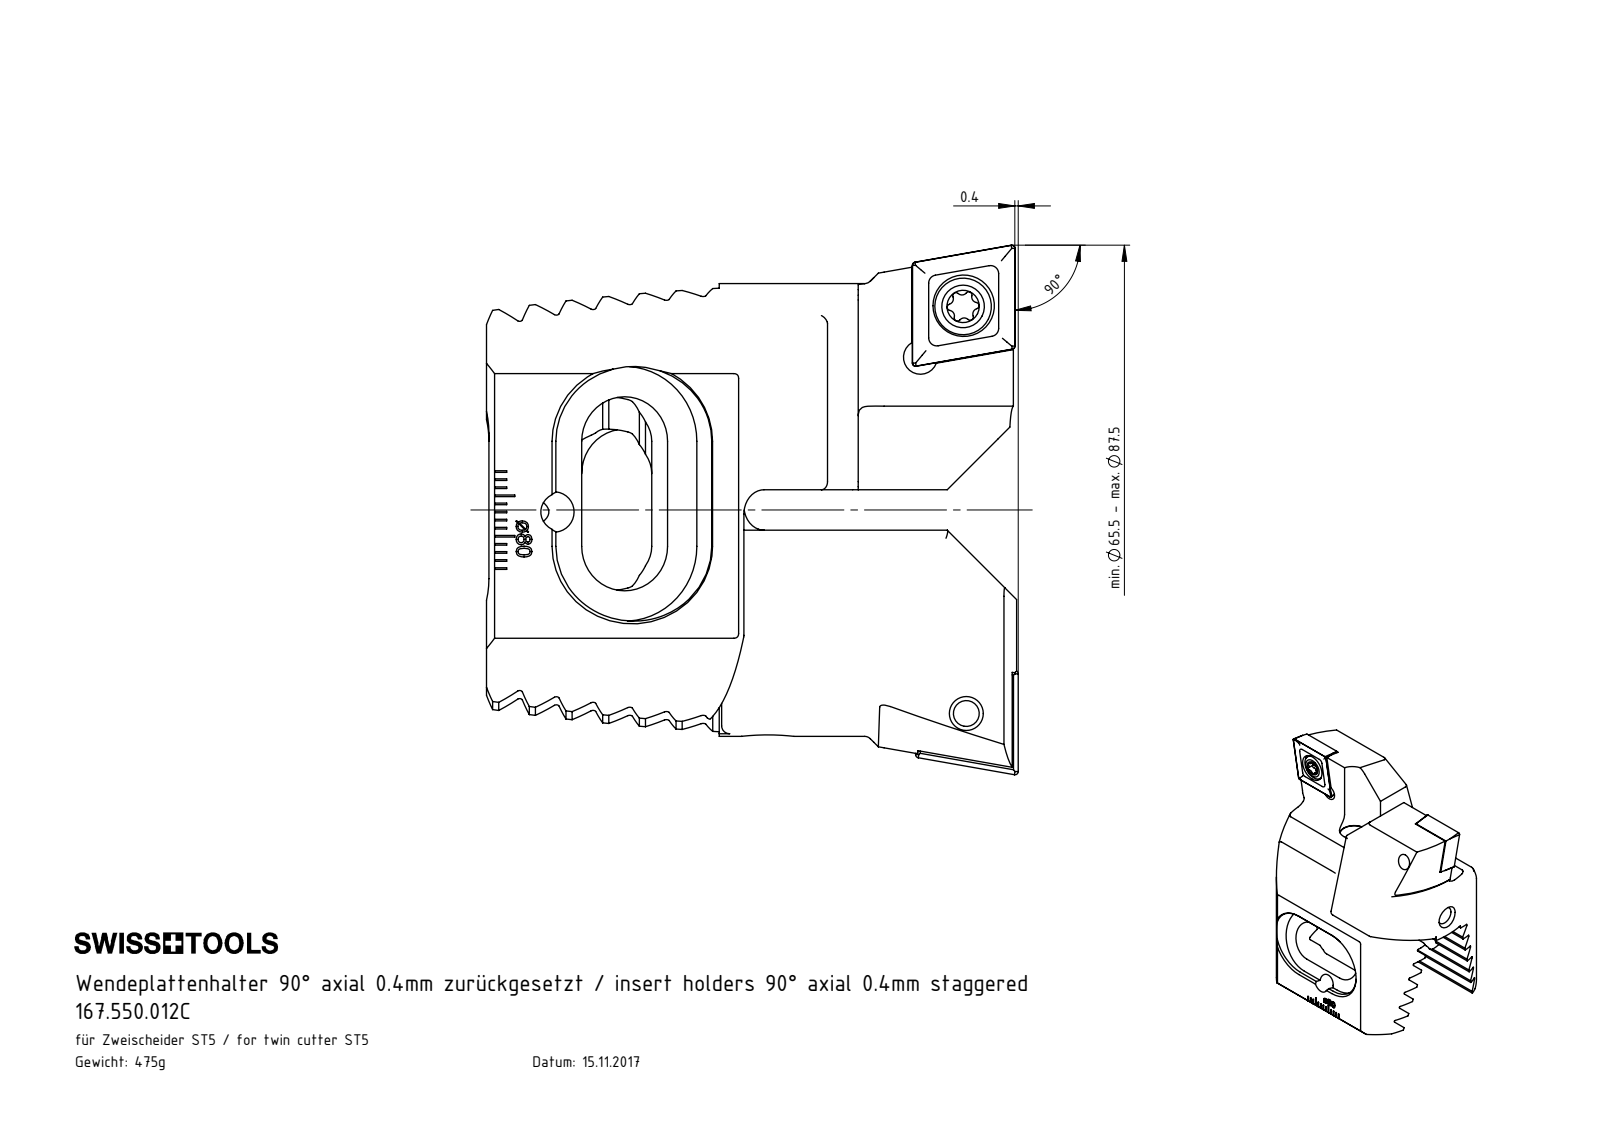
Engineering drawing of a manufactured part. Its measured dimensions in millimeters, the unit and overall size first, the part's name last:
Units: millimetres
Overall size (bounding box): 65.8 × 64.5 × 44.1
Round holes (diameter × count): ⌀4.2 ×4, ⌀2 ×3, ⌀5.5 ×2, ⌀7.6 ×2, ⌀1 ×1, ⌀5 ×1
Round bosses / shafts (diameter × count): ⌀7 ×2, ⌀5 ×2, ⌀6 ×1, ⌀4 ×1
Partial cylindrical surfaces — rounded edges, fillets, slot ends (radius × count): R0.39 ×12, R1 ×11, R0.34 ×6, R0.34 ×6, R0.69 ×6, R0.69 ×6, R3 ×5, R5.5 ×4
Main face-to-face distances: 4.07, 8.14, 12.21, 16.28, 20.35, 5.06, 44.1, 4.46, 4.35, 8.51
Hole centre spacings: 4, 8, 8.21, 8.29, 8.32, 8.5, 15, 16
Volume: 61 717 mm³ · Surface area: 22 861 mm²
Bodies: 8 solids, 560 faces (250 planar, 137 cylindrical, 173 other)
Part name (STEP PRODUCT): 167.550.012C; Z55-WCC.004.037_einzeln; Z55-xxx.001.037_C_versetzt; Z55-ER3.001.020 (+3 more)
STEP written by: SolidWorks 2017 (CONFIG_CONTROL_DESIGN)
